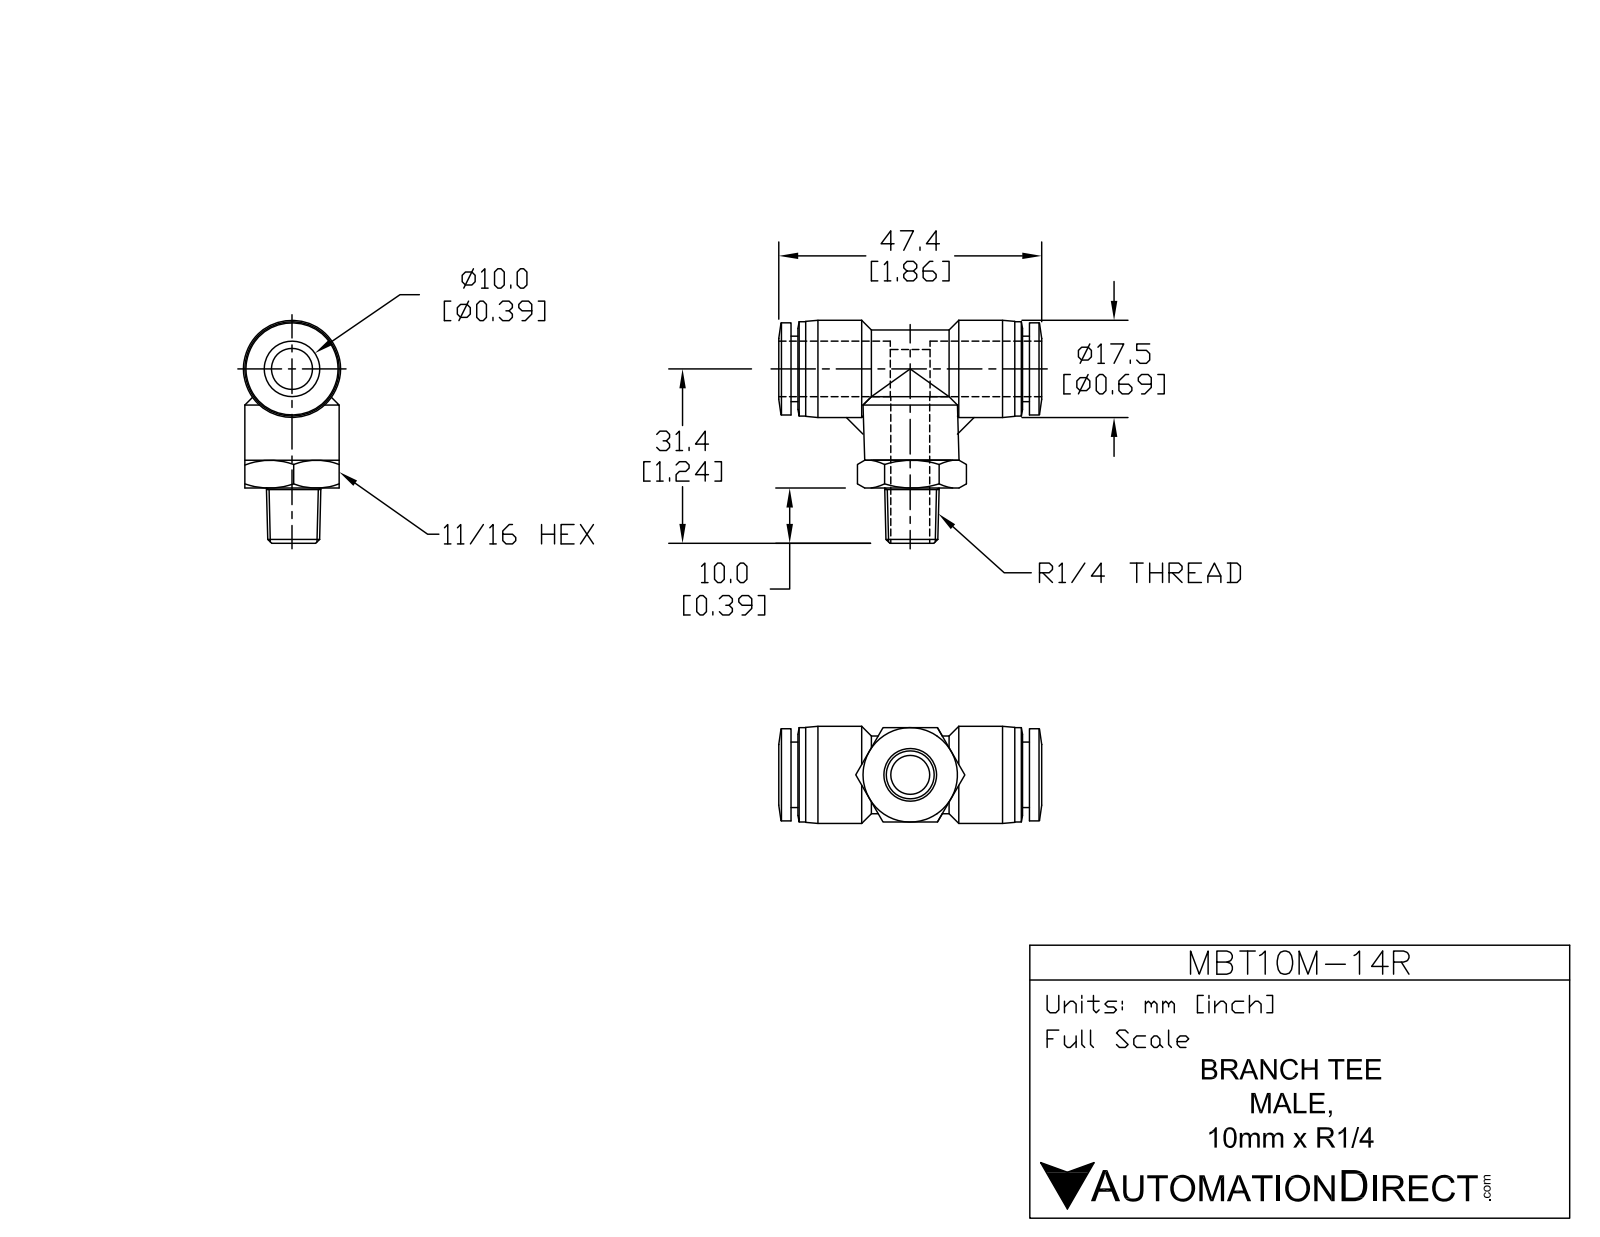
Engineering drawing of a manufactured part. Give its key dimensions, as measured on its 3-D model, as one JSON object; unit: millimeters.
{"part_name": "MBT10M-14R", "step_written_by": "SolidWorks 2015 (AUTOMOTIVE_DESIGN)", "units": "millimeters", "bodies": {"solids": 1, "faces": 102, "planar": 24, "cylindrical": 31, "other": 47}, "overall_size": [50.3, 40.3, 17.5], "volume_mm3": 9770, "surface_area_mm2": 6819, "round_holes": [[8, 2], [10.3, 1]], "round_bosses_or_shafts": [[17, 2], [17.5, 1], [16.6, 1], [14, 1], [11.8, 1]], "partial_cylinders_radius": [[7, 1]], "face_to_face_distances": [17, 1.2, 44.7, 45.9, 18, 27.9, 16.7, 26.6, 43.4, 10]}
